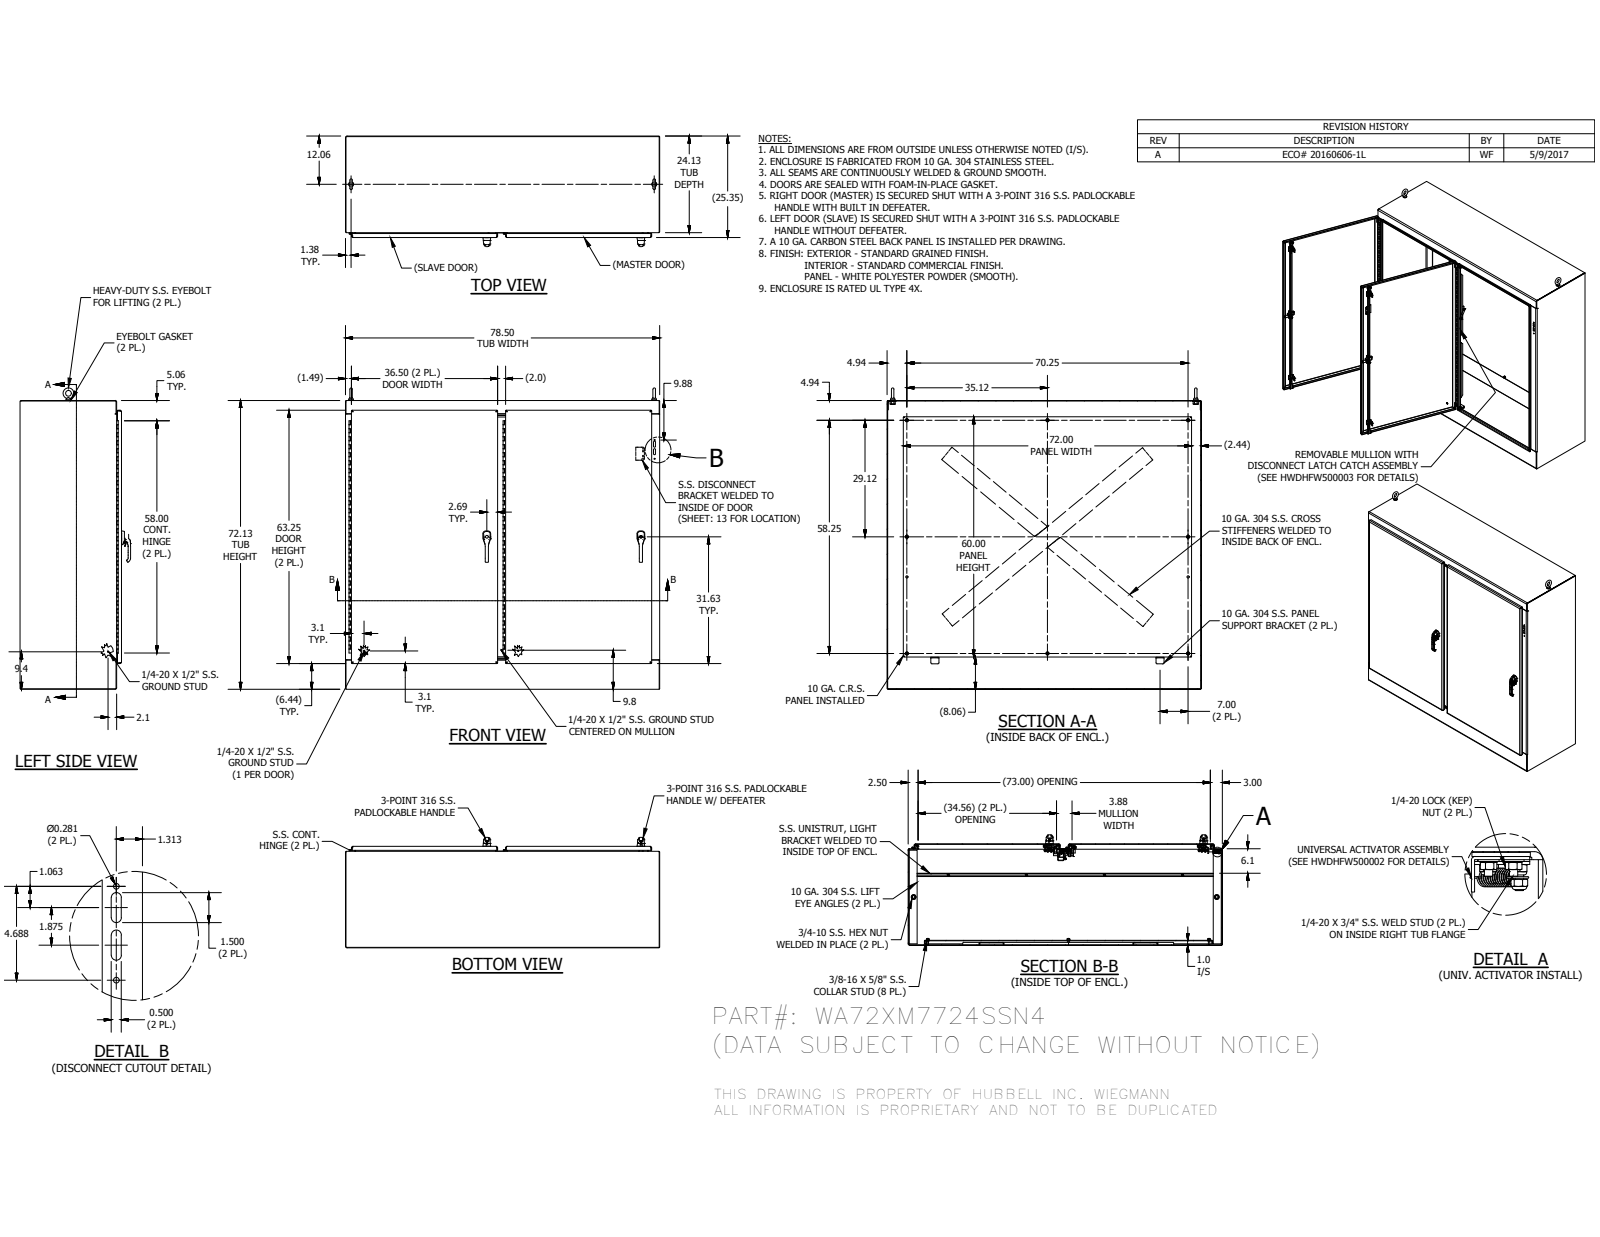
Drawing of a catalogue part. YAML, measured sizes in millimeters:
part_name: "WA72XM7724SSN4BLS; WAXM7724SSN4TOP; WAXM7724SSN4BTM; HFW332010S (+8 more)"
step_written_by: "Autodesk Inventor 2016 (AUTOMOTIVE_DESIGN)"
units: millimeters
bodies: {solids: 256, faces: 10676, planar: 5046, cylindrical: 3502, other: 2128}
overall_size: [1993.9, 1911.29, 701.02]
volume: 57120000
surface_area: 33640000
round_holes:
  - {diameter: 3.55, count: 48}
  - {diameter: 9.52, count: 18}
  - {diameter: 6.35, count: 17}
  - {diameter: 14.29, count: 10}
  - {diameter: 4.76, count: 9}
  - {diameter: 3.45, count: 8}
  - {diameter: 4.17, count: 8}
  - {diameter: 4.83, count: 8}
  - {diameter: 4.98, count: 8}
  - {diameter: 5.1, count: 8}
  - {diameter: 6.65, count: 8}
  - {diameter: 7.33, count: 8}
round_bosses_or_shafts:
  - {diameter: 8.38, count: 18}
  - {diameter: 6.35, count: 18}
  - {diameter: 15.88, count: 13}
  - {diameter: 8.56, count: 12}
  - {diameter: 9.52, count: 11}
  - {diameter: 14.29, count: 9}
  - {diameter: 7.11, count: 8}
  - {diameter: 6.02, count: 8}
partial_cylinders:
  - {radius: 0.5, count: 358}
  - {radius: 0.3, count: 222}
  - {radius: 0.51, count: 192}
  - {radius: 3.17, count: 47}
  - {radius: 0.47, count: 42}
  - {radius: 1.59, count: 36}
  - {radius: 6.35, count: 32}
  - {radius: 1.27, count: 28}
face_to_face_distances: [3.4, 3.41, 640.5, 637.1, 643.9, 25.4, 1828.57, 28.8, 615.1, 32.21]
hole_center_spacings: [973.57, 0.45, 973.64, 973.5, 973.35, 973.42, 973.79, 0.6]
